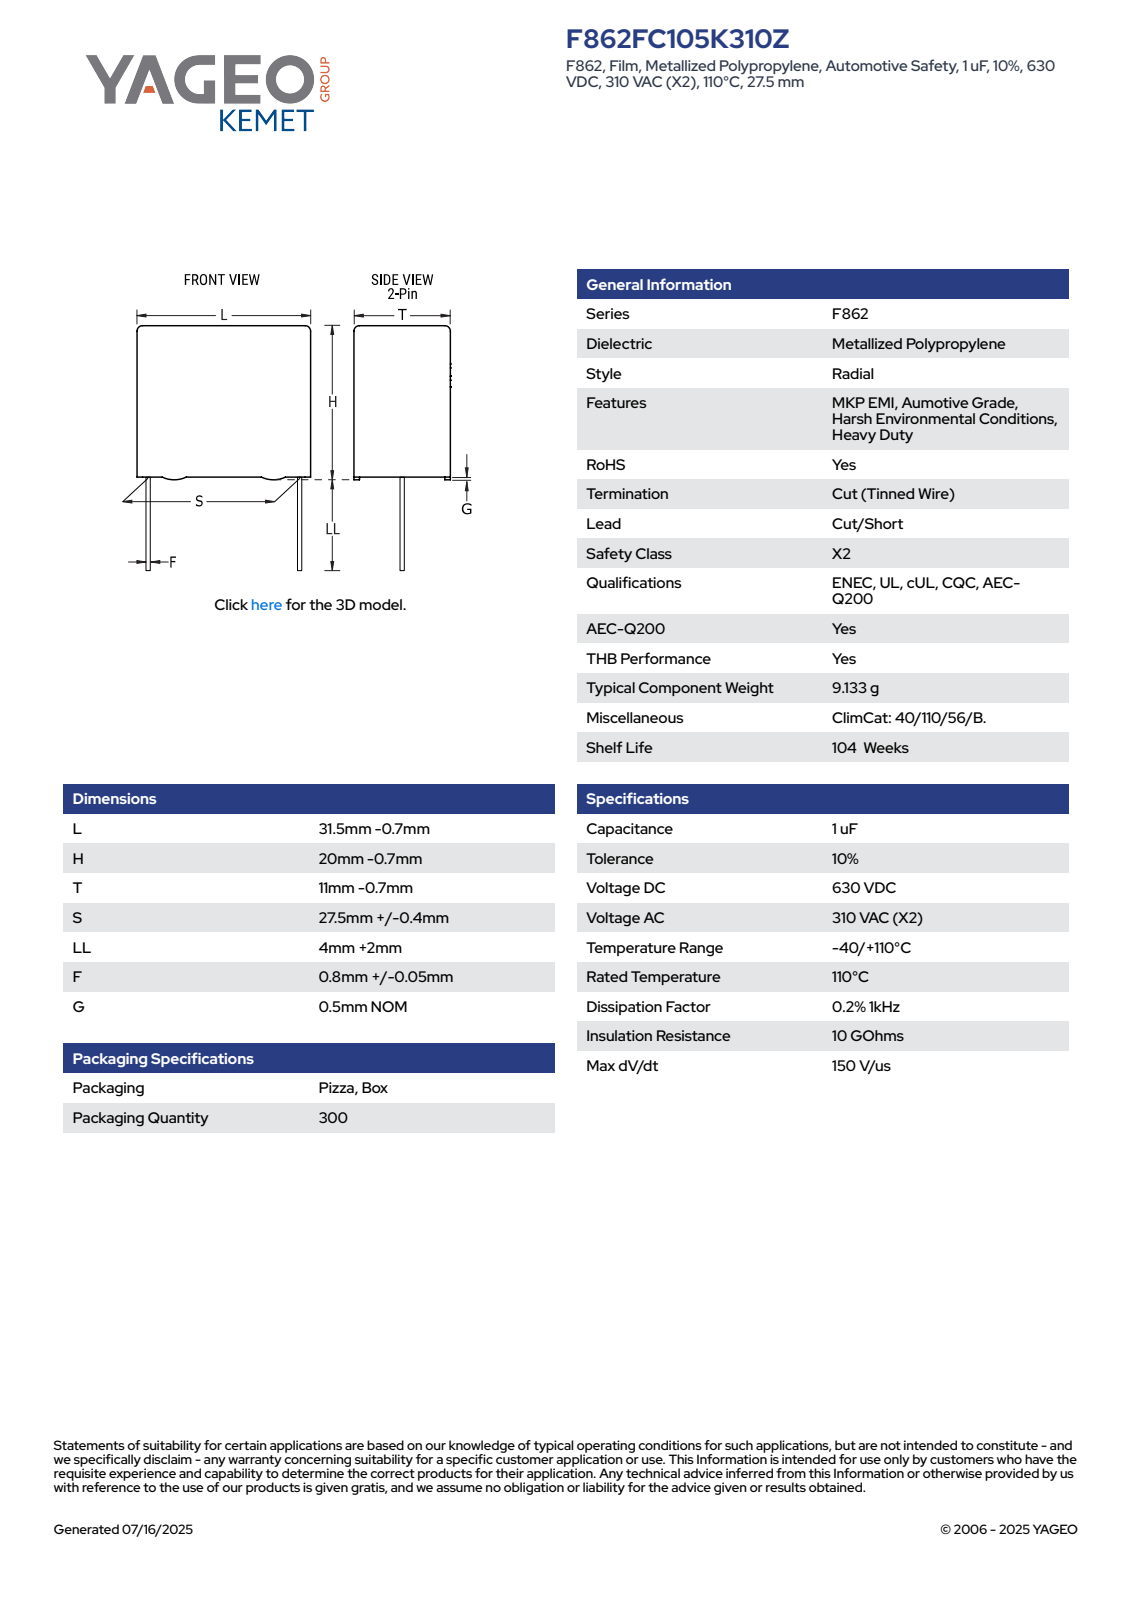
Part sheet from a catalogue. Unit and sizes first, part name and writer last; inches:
Units: inches
Overall size (bounding box): 1.213 × 0.996 × 0.406
Round bosses / shafts (diameter × count): ⌀0.033 ×2
Partial cylindrical surfaces — rounded edges, fillets, slot ends (radius × count): R0.02 ×4
Main face-to-face distances: 0.406, 0.74, 1.213, 0.02, 0.76, 0.023, 0.382, 0.359, 0.236, 0.256
Volume: 0.364 in³ · Surface area: 3.596 in²
Bodies: 4 solids, 89 faces (81 planar, 8 cylindrical, 0 other)
Part name (STEP PRODUCT): CFR_RBG_31.5X20X11_L30.8H19.3T10.3S27.5LL6F0.85G0.5
STEP written by: SolidWorks 2014 (AUTOMOTIVE_DESIGN)
